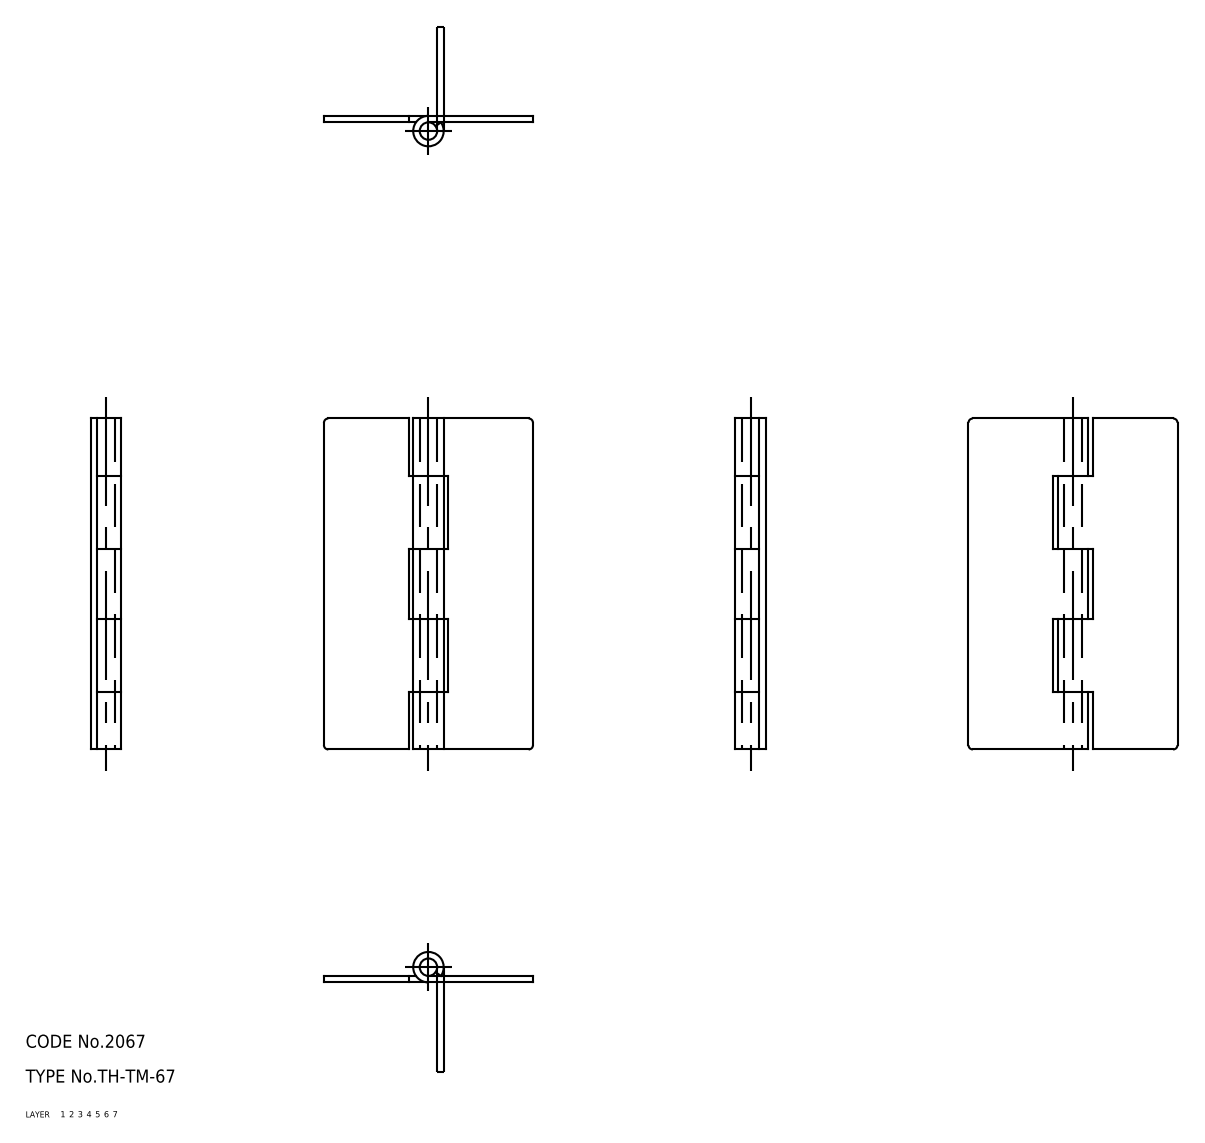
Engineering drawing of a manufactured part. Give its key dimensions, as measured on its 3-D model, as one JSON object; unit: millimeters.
{"part_name": "hinge piece_B; hinge piece_A; shaft; TH_TM_67_24887_36", "step_written_by": "CADfix (AUTOMOTIVE_DESIGN)", "units": "millimeters", "bodies": {"solids": 3, "faces": 46, "planar": 0, "cylindrical": 0, "other": 46}, "overall_size": [76, 48, 7], "volume_mm3": 7577, "surface_area_mm2": 10665}
